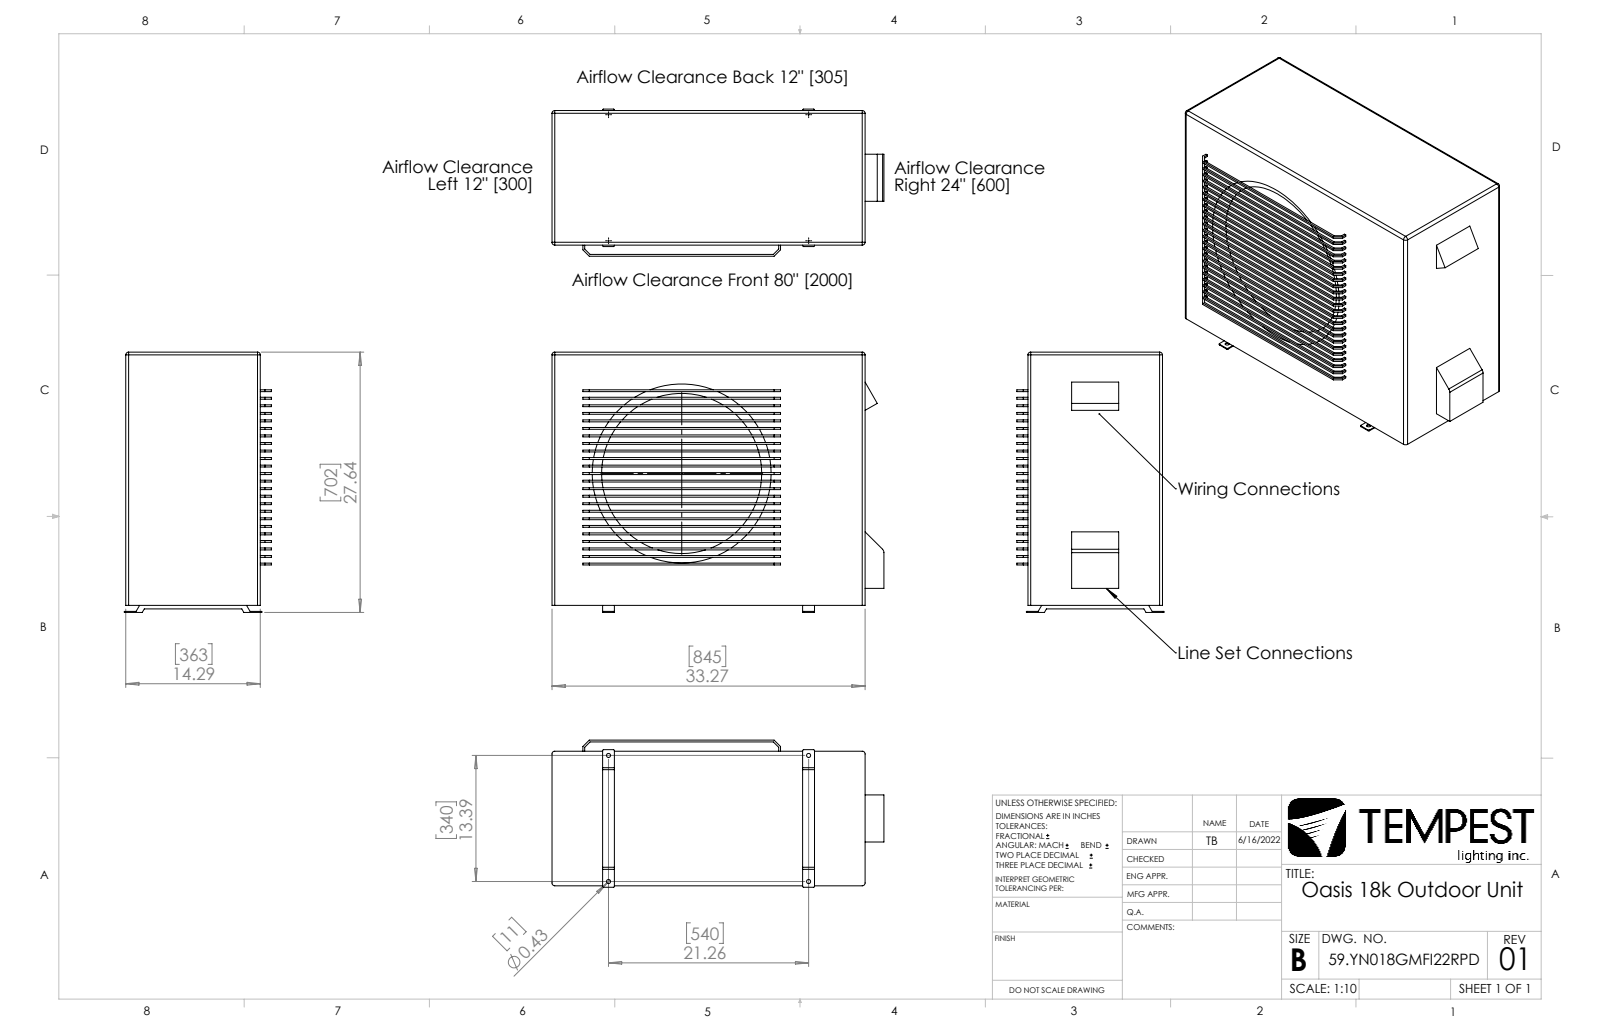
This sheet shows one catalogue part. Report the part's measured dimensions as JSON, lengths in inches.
{"part_name": "59.ODU.LAB; Pioneer ODU Simple_Pioneer 12k ODU - YN012GMFI19RPD; 59.ODU.18 R01", "step_written_by": "SolidWorks 2020 (AUTOMOTIVE_DESIGN)", "units": "inches", "bodies": {"solids": 2, "faces": 1751, "planar": 1354, "cylindrical": 306, "other": 91}, "overall_size": [34.975, 22, 14.5], "volume_in3": 3547, "surface_area_in2": 5022, "round_holes": [[0.875, 2], [0.835, 1], [17, 1]], "round_bosses_or_shafts": [[4, 1]], "partial_cylinders_radius": [[0.25, 104], [0.1, 47], [0.107, 18], [0.75, 12], [0.05, 10], [1, 9], [0.233, 8], [0.685, 8]], "face_to_face_distances": [1.5, 1.25, 20, 12.025, 10.525, 0.2, 2.875, 9.15, 7.65, 0.1], "hole_center_spacings": [1.5]}
